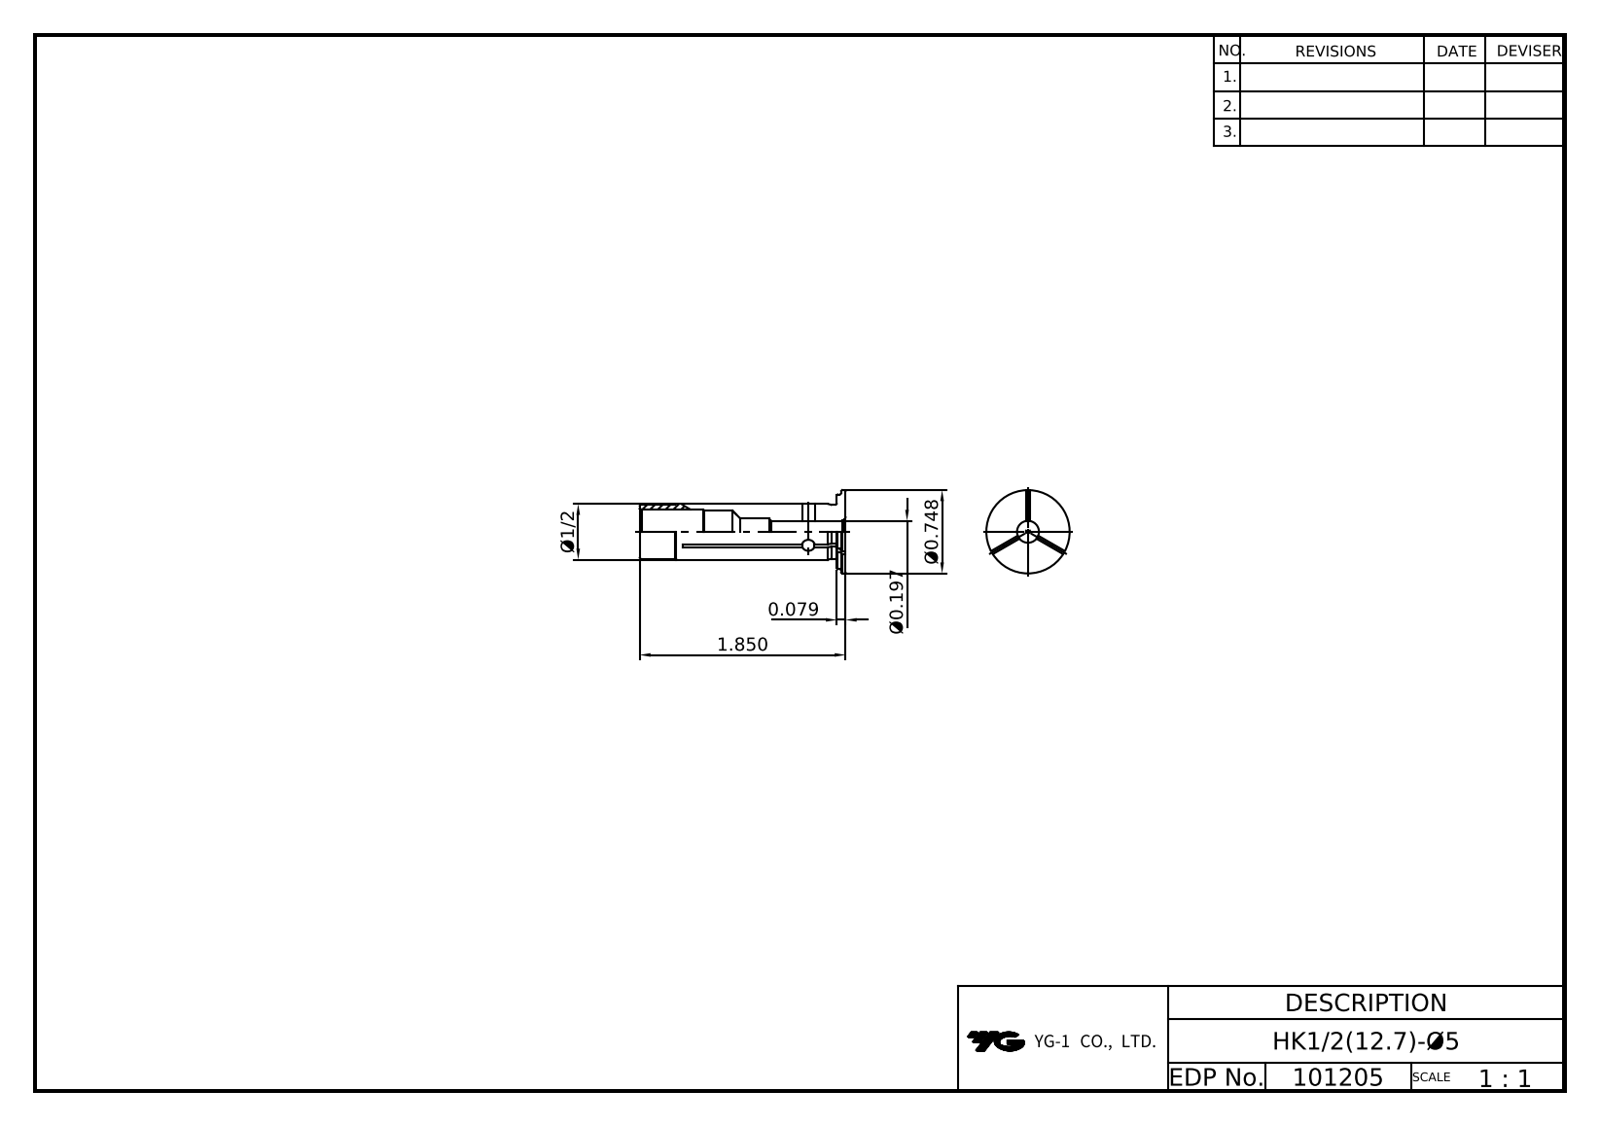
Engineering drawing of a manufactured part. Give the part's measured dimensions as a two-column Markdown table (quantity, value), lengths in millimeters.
| quantity | value |
| --- | --- |
| part name | LO-HK12.7-5 |
| STEP written by | Autodesk Inventor 2025 (AP242_MANAGED_MODEL_BASED_3D_ENGINEERING_MIM_LF) |
| units | millimeters |
| bodies | 1 solid, 14 faces (4 planar, 7 cylindrical, 3 other) |
| overall size | 47 × 19 × 19 |
| volume | 3 970 mm³ |
| surface area | 3 502 mm² |
| round holes (diameter × count) | 5 × 1, 6 × 1, 9.6 × 1, 10 × 1 |
| round bosses / shafts (diameter × count) | 19 × 1, 17 × 1, 12.7 × 1 |
| main face-to-face distances | 1, 2, 45, 46, 47 |
